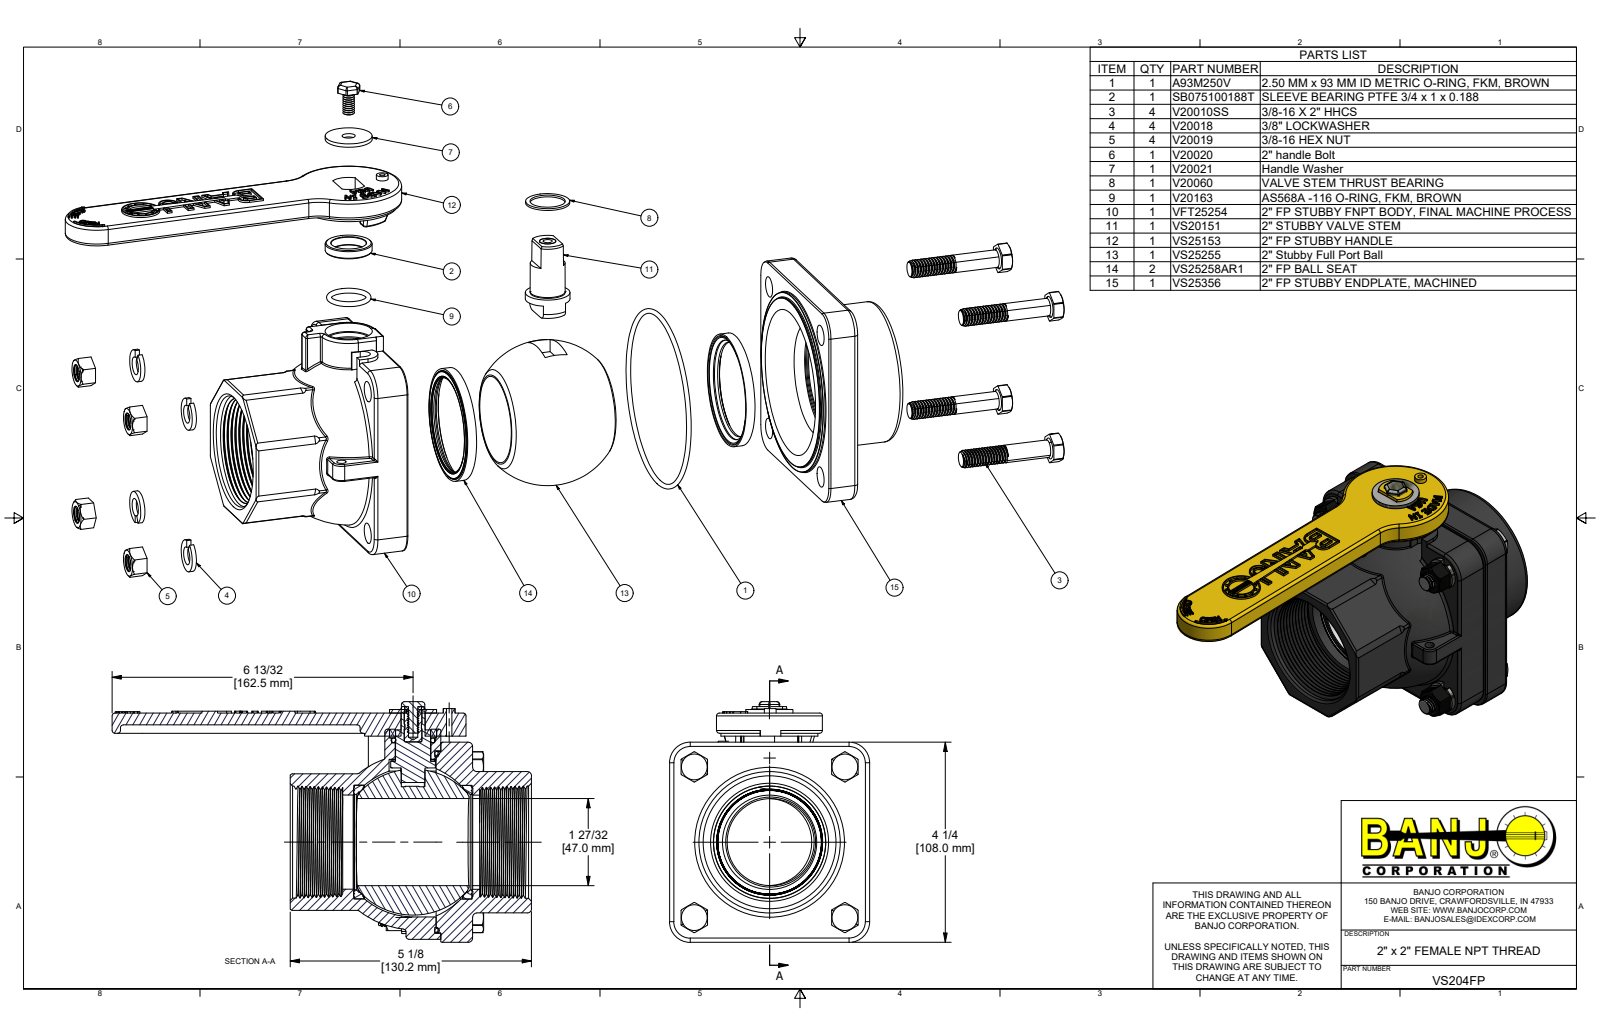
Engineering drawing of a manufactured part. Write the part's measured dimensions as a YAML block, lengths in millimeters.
part_name: "VS204FP; VFT25254; VFT25254Y; VFT25254X (+8 more)"
step_written_by: "Autodesk Inventor 2022 (AUTOMOTIVE_DESIGN)"
units: millimeters
bodies: {solids: 26, faces: 1971, planar: 619, cylindrical: 592, other: 760}
overall_size: [226.7, 129.8, 108]
volume: 651900
surface_area: 190800
round_holes:
  - {diameter: 9.5, count: 5}
  - {diameter: 7.8, count: 4}
  - {diameter: 9.8, count: 4}
  - {diameter: 11.1, count: 4}
  - {diameter: 11.2, count: 4}
  - {diameter: 5.1, count: 2}
  - {diameter: 50.8, count: 2}
  - {diameter: 51.4, count: 2}
  - {diameter: 54.1, count: 2}
  - {diameter: 61.4, count: 2}
  - {diameter: 3, count: 1}
  - {diameter: 5, count: 1}
round_bosses_or_shafts:
  - {diameter: 8.2, count: 60}
  - {diameter: 17.4, count: 4}
  - {diameter: 9.5, count: 4}
  - {diameter: 92.1, count: 2}
  - {diameter: 61.3, count: 2}
  - {diameter: 97.8, count: 1}
  - {diameter: 76.2, count: 1}
  - {diameter: 57.2, count: 1}
partial_cylinders:
  - {radius: 1.5, count: 41}
  - {radius: 0.8, count: 23}
  - {radius: 2.3, count: 16}
  - {radius: 4.1, count: 8}
  - {radius: 8.1, count: 4}
  - {radius: 11.1, count: 4}
  - {radius: 11.9, count: 4}
  - {radius: 0.4, count: 3}
face_to_face_distances: [17.1, 89.3, 15.6, 2.5, 19.7, 35.9, 18.8, 16.3, 6.4, 1.6]
hole_center_spacings: [57.5, 81.3, 115, 81.2, 81.4, 51.8, 57.4, 57.6]
